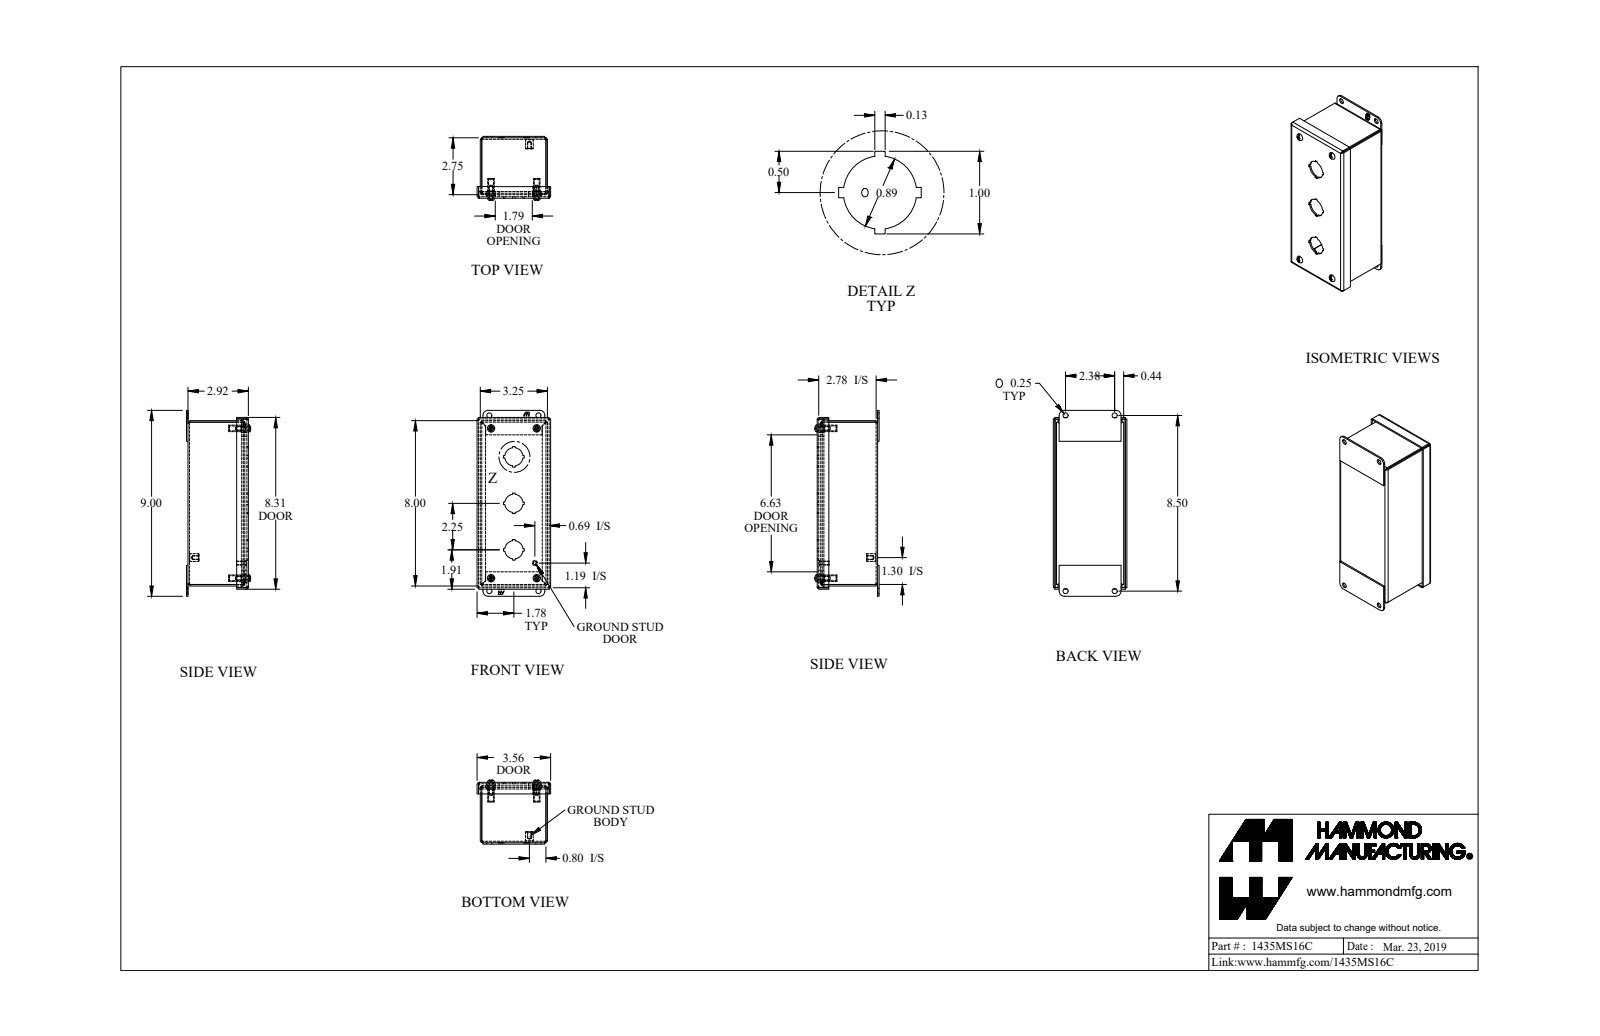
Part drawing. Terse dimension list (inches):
name: 1435MS16C_Default
written by: SolidWorks 2019 (CONFIG_CONTROL_DESIGN)
unit: in
bodies: 19 solids, 493 faces (319 planar, 144 cylindrical, 30 other)
size: 9 × 3.562 × 3.104
volume: 12.23 in³; area: 320.6 in²
holes: 8× ⌀0.25, 4× ⌀0.065, 4× ⌀0.239, 4× ⌀0.253, 4× ⌀0.406, 3× ⌀0.886, 1× ⌀0.156
bosses: 5× ⌀0.19, 4× ⌀0.406, 4× ⌀0.315, 4× ⌀0.148, 1× ⌀0.375, 1× ⌀0.25
rounds: 12× R0.036, 12× R0.108, 4× R0.171, 4× R0.25, 1× R0.125
face distances: 0.072, 2.85, 0.072, 3.178, 2.922, 2.778, 3.106, 3.25, 7.928, 0.156
hole spacings: 7.25, 2.211, 7.58, 7.876, 2.212, 0.63, 0.63, 2.377
